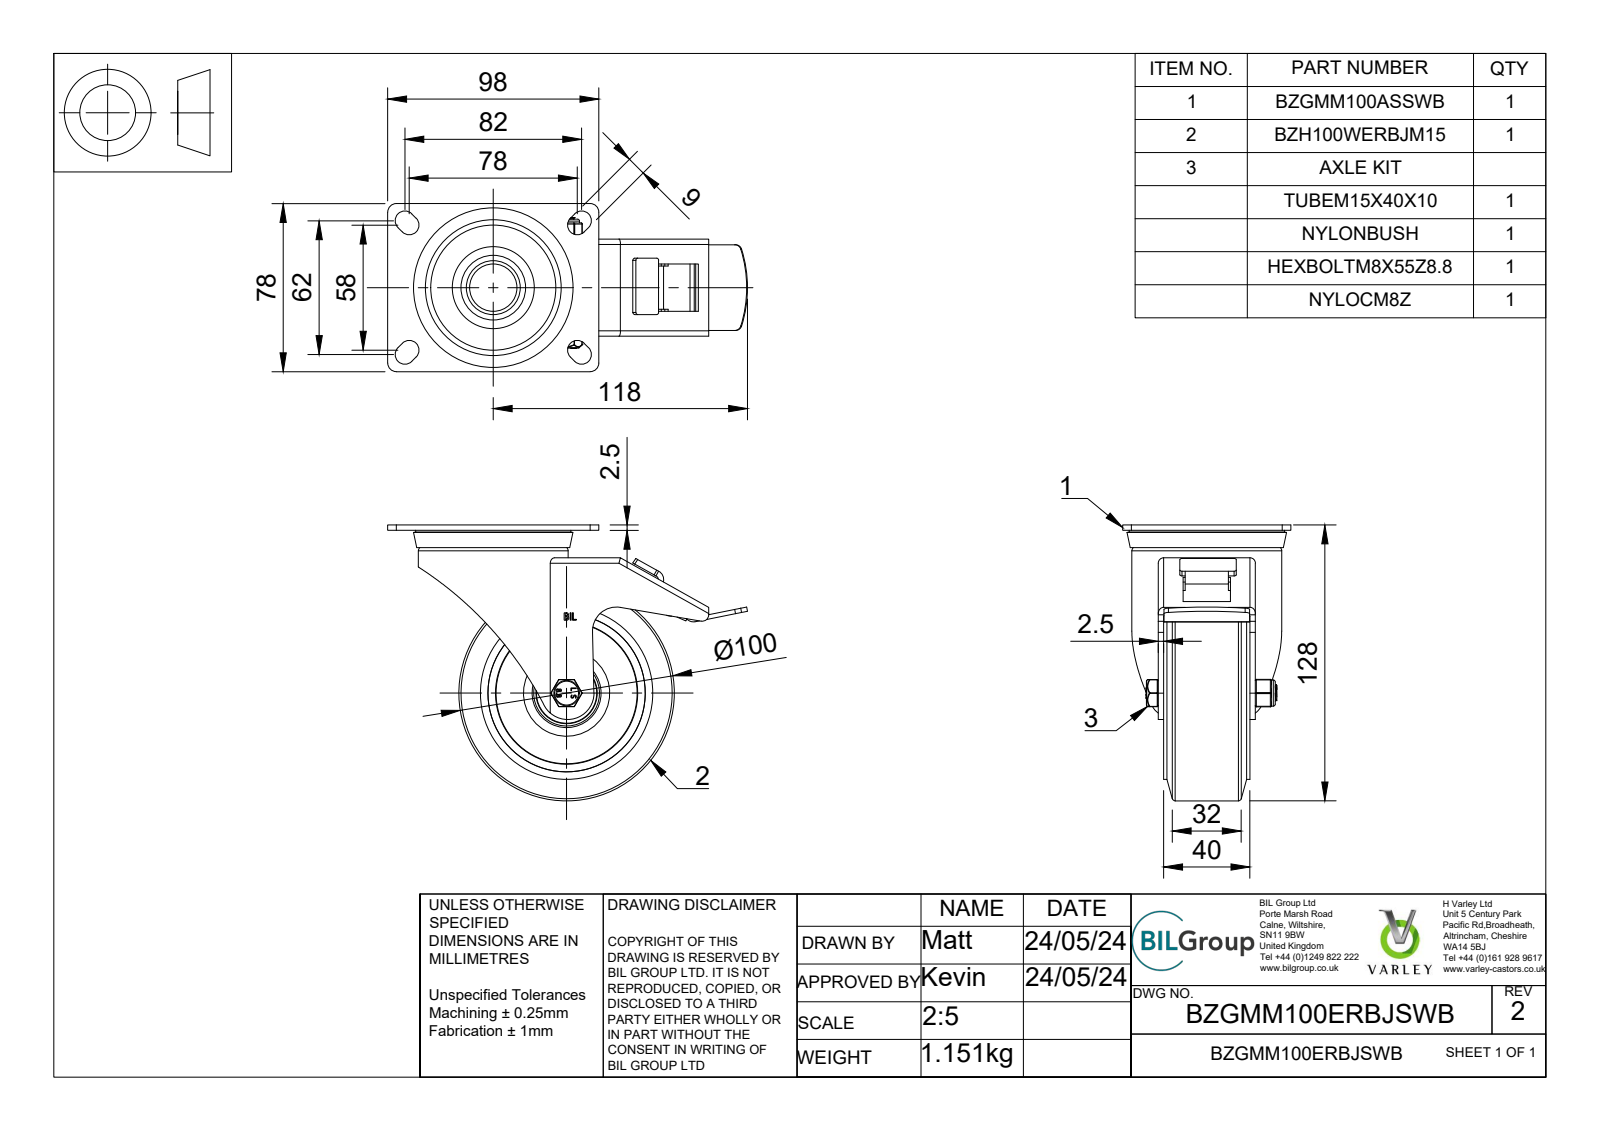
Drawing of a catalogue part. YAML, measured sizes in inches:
part_name: "BZGMM100ERBJSWB v3; BZGMM100ASSWB - 2 v1; ZINC PLATED, PRESSED STEEL FORKS; BRAKE PAD (+7 more)"
step_written_by: "Autodesk Translation Framework v13.14.0.145 (AUTOMOTIVE_DESIGN)"
units: inches
bodies: {solids: 69, faces: 1187, planar: 502, cylindrical: 238, other: 447}
overall_size: [6.575, 5.039, 3.071]
volume: 19.5
surface_area: 239.8
round_holes:
  - {diameter: 0.026, count: 2}
  - {diameter: 0.315, count: 1}
  - {diameter: 0.323, count: 1}
  - {diameter: 0.339, count: 1}
  - {diameter: 0.402, count: 1}
  - {diameter: 0.591, count: 1}
  - {diameter: 0.709, count: 1}
  - {diameter: 0.787, count: 1}
  - {diameter: 0.827, count: 1}
  - {diameter: 1.024, count: 1}
  - {diameter: 1.079, count: 1}
  - {diameter: 1.181, count: 1}
round_bosses_or_shafts:
  - {diameter: 3.937, count: 1}
  - {diameter: 3.15, count: 1}
  - {diameter: 2.736, count: 1}
  - {diameter: 1.85, count: 1}
  - {diameter: 1.575, count: 1}
  - {diameter: 1.118, count: 1}
  - {diameter: 1.102, count: 1}
  - {diameter: 0.984, count: 1}
partial_cylinders:
  - {radius: 0.02, count: 18}
  - {radius: 0.01, count: 12}
  - {radius: 0.049, count: 8}
  - {radius: 0.177, count: 8}
  - {radius: 0.157, count: 5}
  - {radius: 0.013, count: 4}
  - {radius: 0.025, count: 4}
  - {radius: 0.039, count: 4}
face_to_face_distances: [0.098, 1.575, 1.673, 0.728, 1.043, 0.63, 0.945, 0.118, 0.315, 1.22]
hole_center_spacings: [0.127, 0.098]
